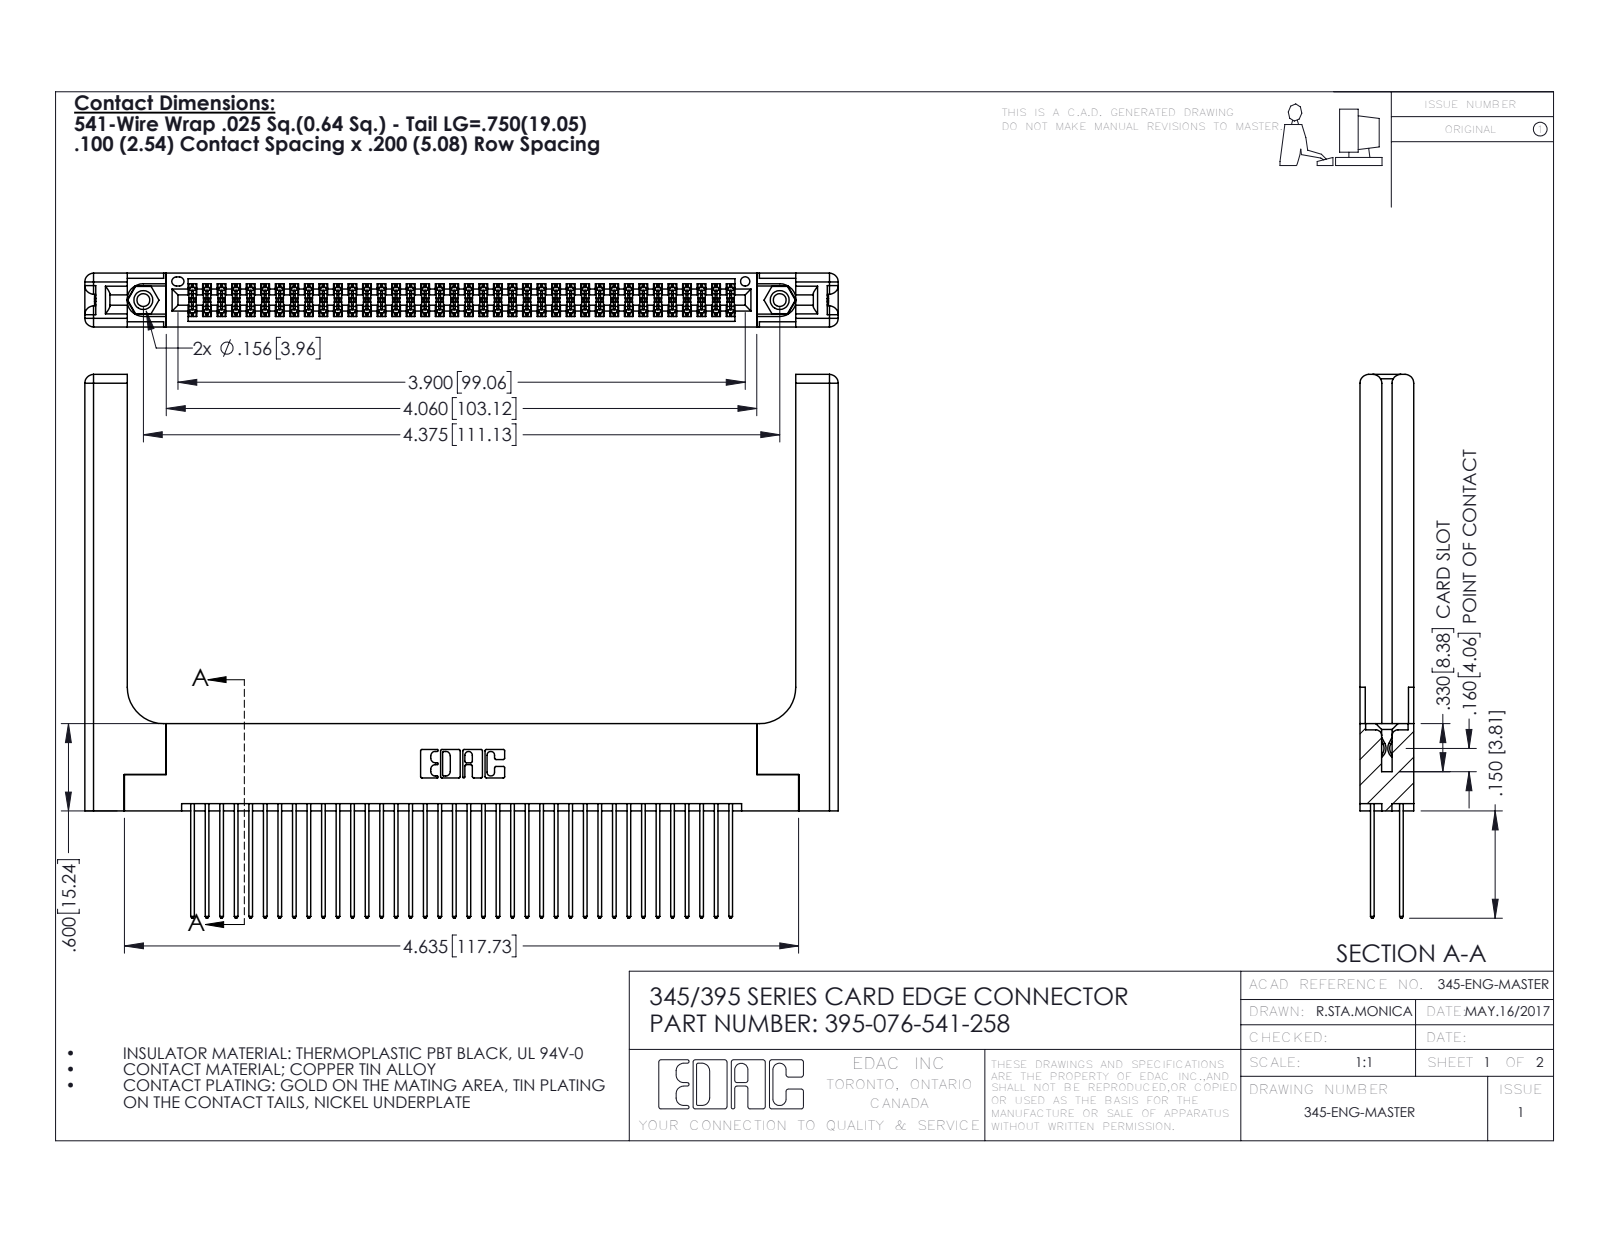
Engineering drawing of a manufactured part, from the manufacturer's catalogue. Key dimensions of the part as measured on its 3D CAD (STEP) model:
Part name (STEP PRODUCT): 395-076-541-258; 345-250-001_345-250-001-102; 345-292-001_345-293-141; 345 Part_Flush Mounting Lugs - 0.156 Dia-TH (+1 more)
STEP written by: SolidWorks 2016 (CONFIG_CONTROL_DESIGN)
Units: inches
Bodies: 81 solids, 4182 faces (2736 planar, 1386 cylindrical, 60 other)
Overall size (bounding box): 5.179 × 3.737 × 0.37
Volume: 1.321 in³ · Surface area: 41.09 in²
Round holes (diameter × count): ⌀0.089 ×2, ⌀0.125 ×2, ⌀0.156 ×2, ⌀0.064 ×1
Round bosses / shafts (diameter × count): ⌀0.155 ×2
Partial cylindrical surfaces — rounded edges, fillets, slot ends (radius × count): R0.006 ×114, R0.01 ×76, R0.01 ×22, R0.06 ×16, R0.007 ×6, R0.031 ×6, R0.026 ×3, R0.014 ×2
Main face-to-face distances: 0.072, 0.298, 0.37, 0.2, 0.098, 0.272, 0.025, 0.225, 0.175, 0.148
Hole centre spacings: 0.27, 4.139, 4.375
